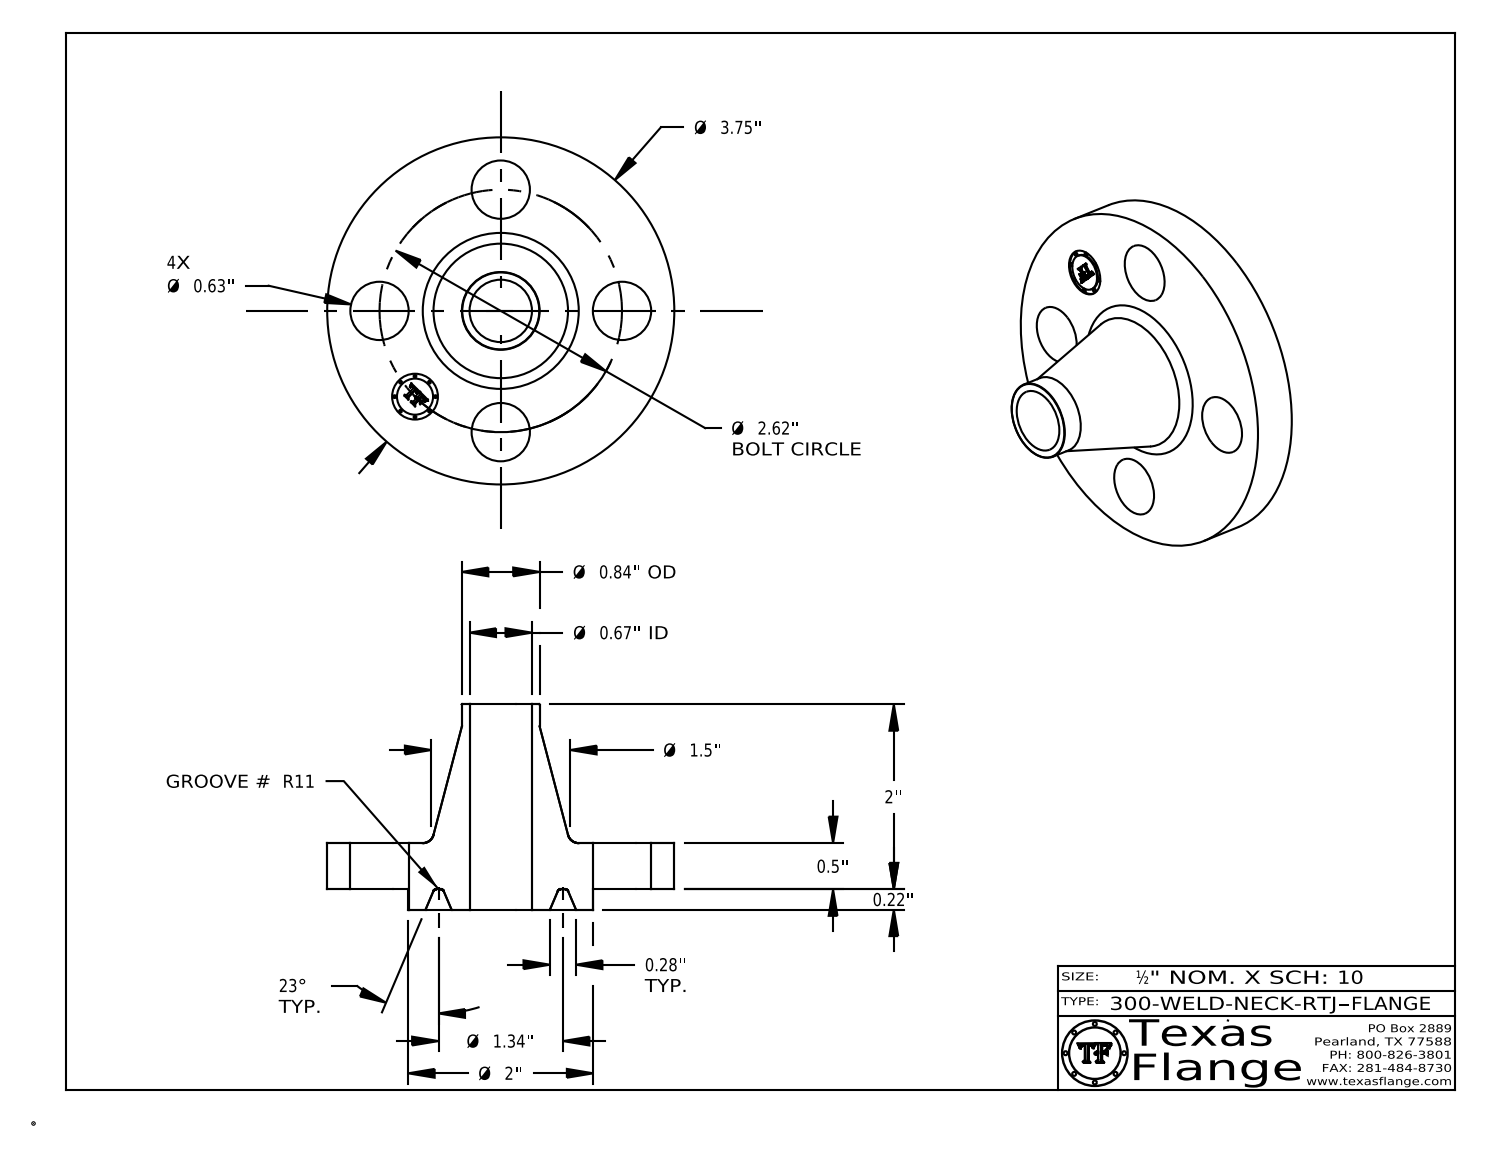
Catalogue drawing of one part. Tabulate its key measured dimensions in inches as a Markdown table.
| quantity | value |
| --- | --- |
| part name | 300-WELD-NECK-RTJ |
| STEP written by | CATIA V5 STEP AP214 (AUTOMOTIVE_DESIGN) |
| units | inches |
| bodies | 1 solid, 425 faces (371 planar, 40 cylindrical, 14 other) |
| overall size | 3.75 × 3.75 × 2.219 |
| volume | 6.152 in³ |
| surface area | 40.16 in² |
| round holes (diameter × count) | 0.63 × 4, 0.495 × 1, 0.674 × 1 |
| round bosses / shafts (diameter × count) | 0.03 × 8, 3.75 × 1, 2 × 1, 0.84 × 1, 0.39 × 1 |
| main face-to-face distances | 0.5, 0.219, 0.719, 2.219, 2, 1.5, 0.704, 0.485, 0.015, 1.515 |
| hole center spacings | 1.31, 1.852, 1.003, 2.42, 2.62, 1.31 |
